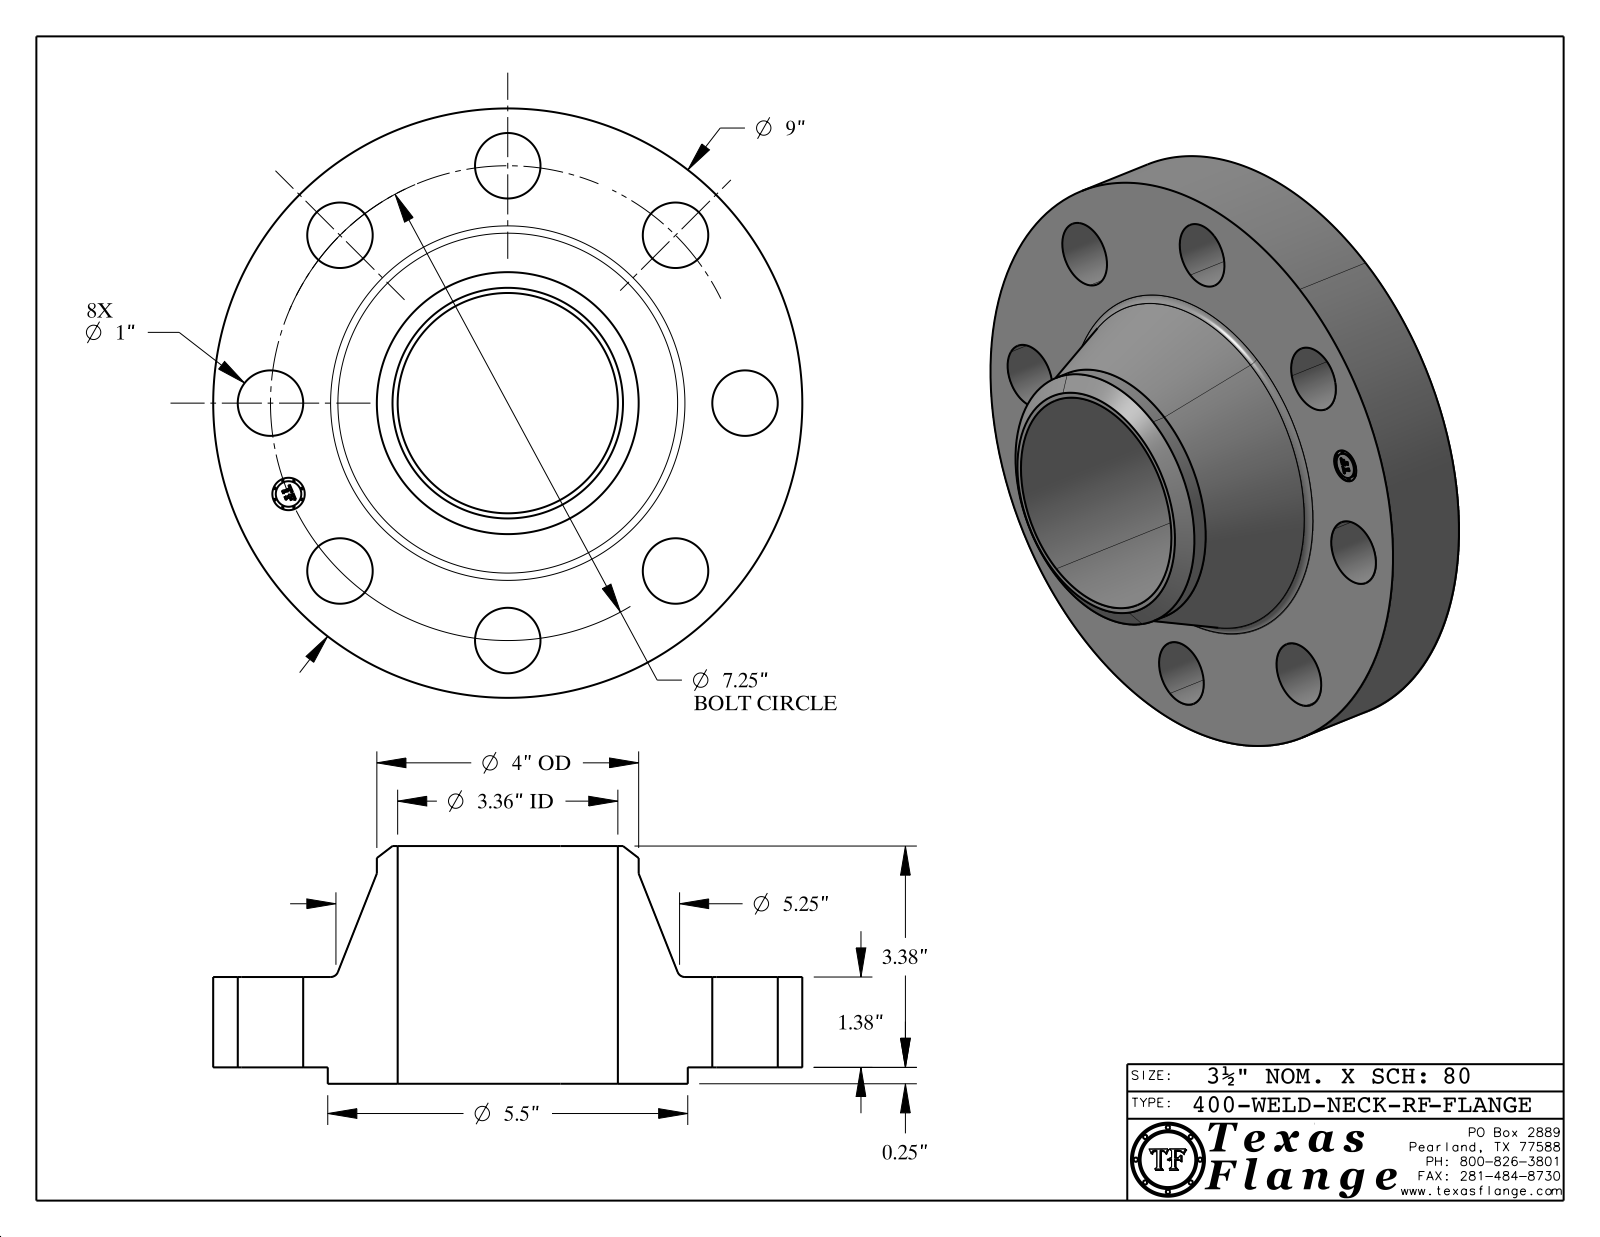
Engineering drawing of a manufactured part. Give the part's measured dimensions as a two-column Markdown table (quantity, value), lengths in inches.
| quantity | value |
| --- | --- |
| part name | 400-WELD-NECK-RF |
| STEP written by | CATIA V5 STEP AP214 (AUTOMOTIVE_DESIGN) |
| units | inches |
| bodies | 1 solid, 419 faces (369 planar, 44 cylindrical, 6 other) |
| overall size | 9 × 9 × 3.63 |
| volume | 84.54 in³ |
| surface area | 232.4 in² |
| round holes (diameter × count) | 1 × 8, 0.495 × 1, 3.364 × 1 |
| round bosses / shafts (diameter × count) | 0.03 × 8, 9 × 1, 5.5 × 1, 4 × 1, 0.39 × 1 |
| main face-to-face distances | 1.38, 0.25, 1.63, 3.63, 3.38, 2, 1.615, 1.365, 0.015, 2.015 |
| hole center spacings | 3.625, 2.774, 5.127, 6.698, 7.25, 1.415, 7.111, 4.028 |
